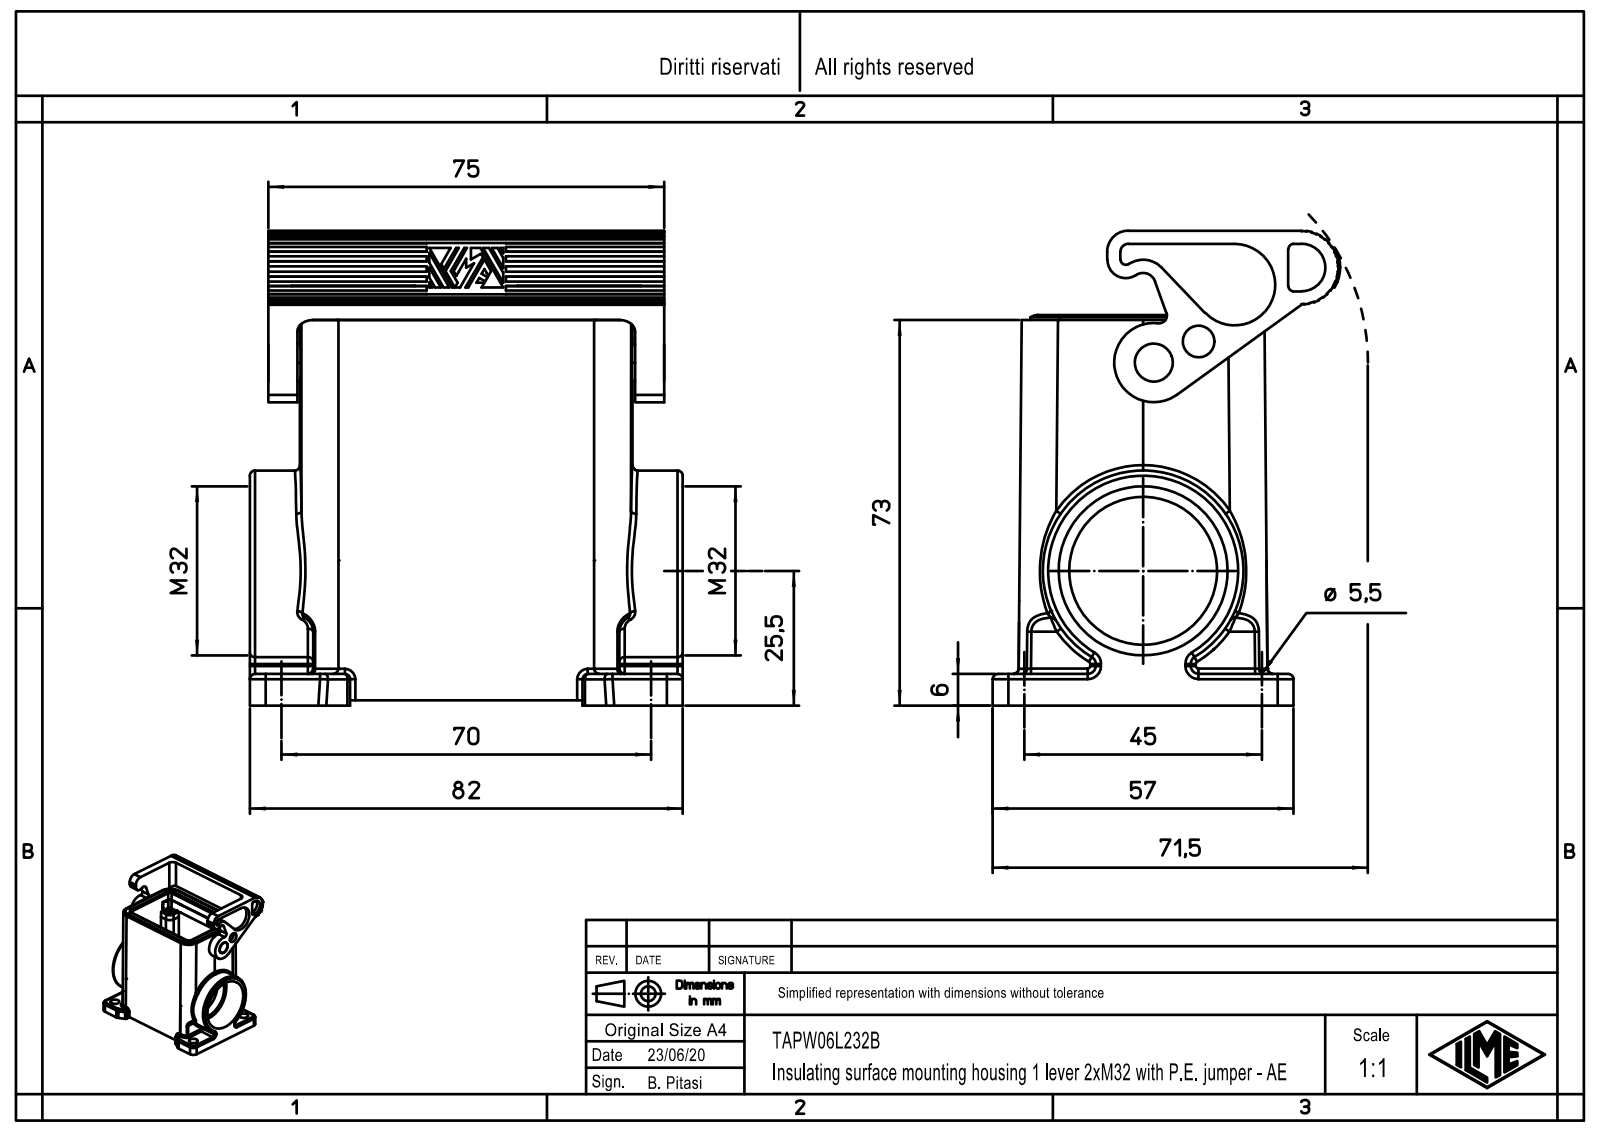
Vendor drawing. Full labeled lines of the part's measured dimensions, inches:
Part name (STEP PRODUCT): TAPW06L232B
STEP written by: Creo Elements/Direct Modeling 20.1B 02-Apr-2019 (C) Parametric Technology GmbH (AUTOMOTIVE_DESIGN)
Units: inches
Bodies: 1 solid, 780 faces (399 planar, 227 cylindrical, 154 other)
Overall size (bounding box): 3.539 × 3.228 × 2.591
Volume: 7.63 in³ · Surface area: 77.53 in²
Round holes (diameter × count): ⌀0.118 ×4, ⌀0.138 ×4, ⌀0.217 ×4, ⌀0.236 ×1, ⌀0.394 ×1, ⌀1.102 ×1, ⌀1.26 ×1
Round bosses / shafts (diameter × count): ⌀0.189 ×4, ⌀1.496 ×1, ⌀0.276 ×1
Partial cylindrical surfaces — rounded edges, fillets, slot ends (radius × count): R0.039 ×32, R0.059 ×18, R0.118 ×12, R0.138 ×5, R0.276 ×5, R0.02 ×4, R0.051 ×4, R0.063 ×4
Main face-to-face distances: 1.598, 0.217, 0.236, 0.039, 2.874, 2.638, 0.354, 0.256, 0.118, 0.02
Hole centre spacings: 0.622, 1.507, 2.272, 2.654, 1.063, 1.732, 1.772, 2.032
